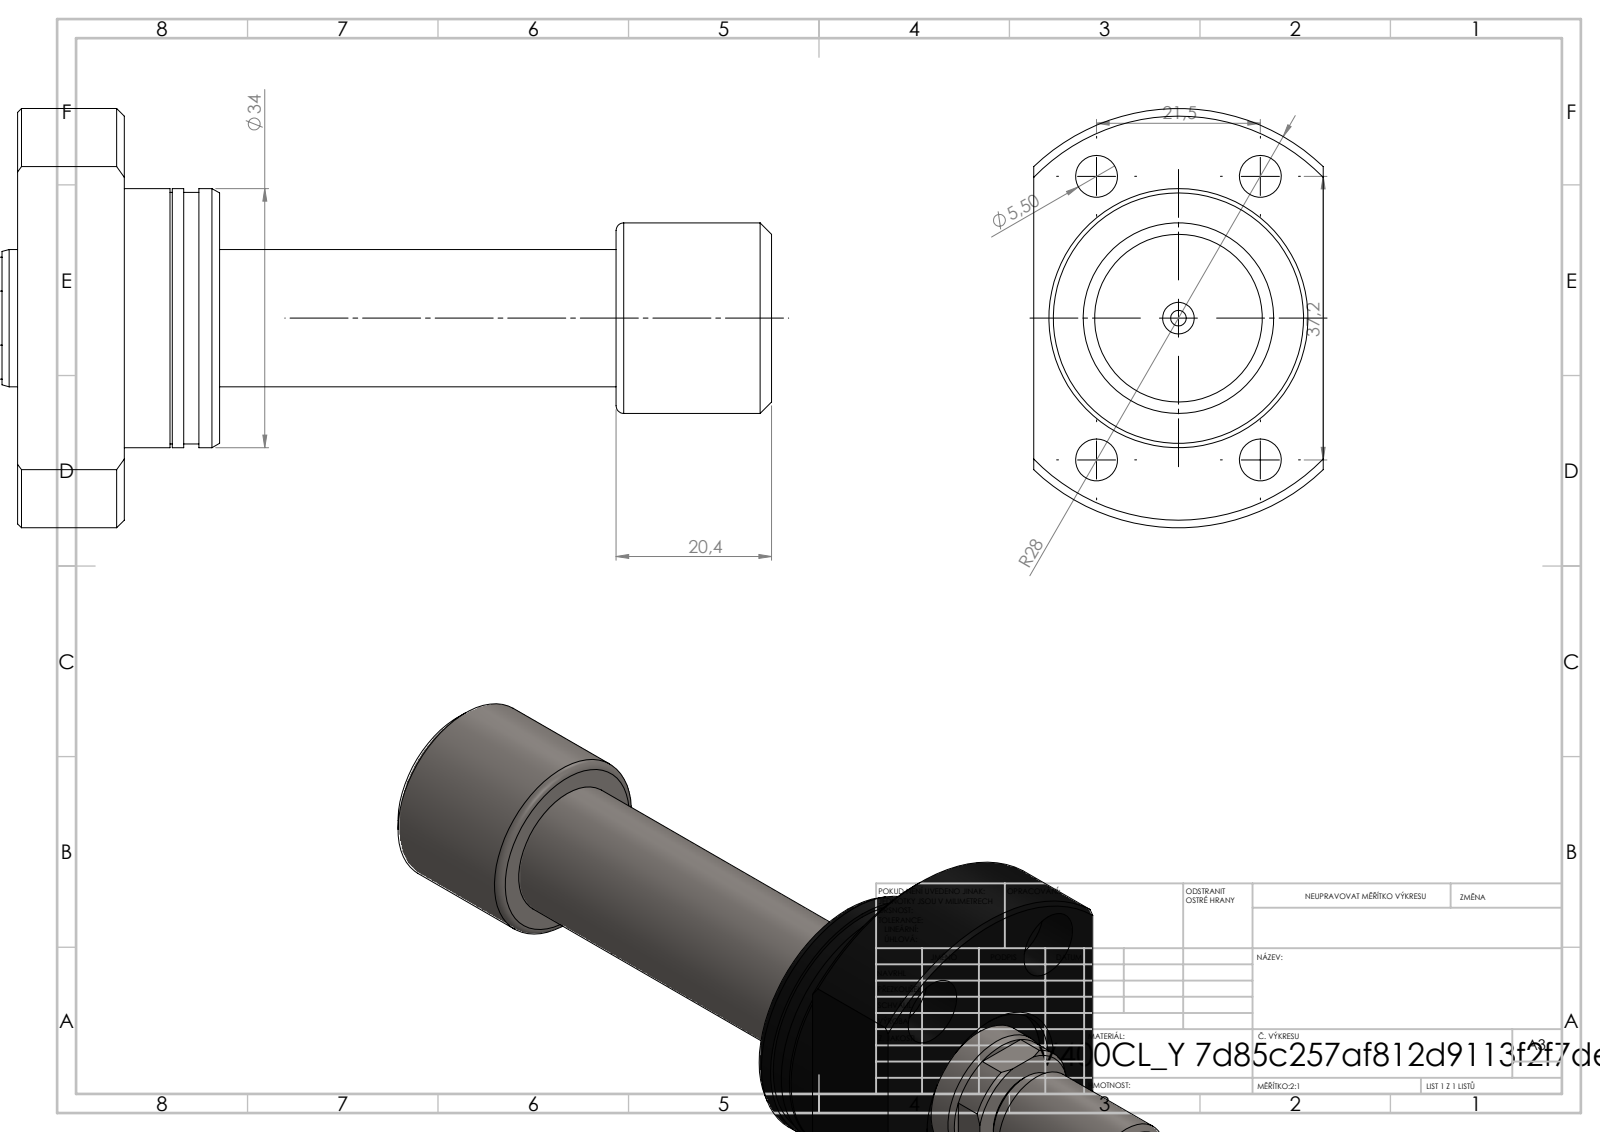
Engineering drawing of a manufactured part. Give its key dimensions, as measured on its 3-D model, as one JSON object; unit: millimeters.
{"part_name": "V400CL_PC_Y; V450CM_MALE_METRIC; V400CL_VC_X", "step_written_by": "SolidWorks 2019 (CONFIG_CONTROL_DESIGN)", "units": "millimeters", "bodies": {"solids": 3, "faces": 117, "planar": 30, "cylindrical": 53, "other": 34}, "overall_size": [125, 55, 38], "volume_mm3": 62296, "surface_area_mm2": 18281, "round_holes": [[5.5, 4], [9, 4], [2.05, 1], [5, 1], [6, 1], [18, 1], [22.5, 1]], "round_bosses_or_shafts": [[34, 1], [33, 1], [25, 1], [14, 1], [12, 1], [11, 1]], "partial_cylinders_radius": [[8.75, 1], [27.5, 1]], "face_to_face_distances": [14, 38, 12.5, 26.5, 72.45, 84.95, 98.95, 105, 32.55, 20.05], "hole_center_spacings": [21.48, 21.5, 37.2, 42.97]}
